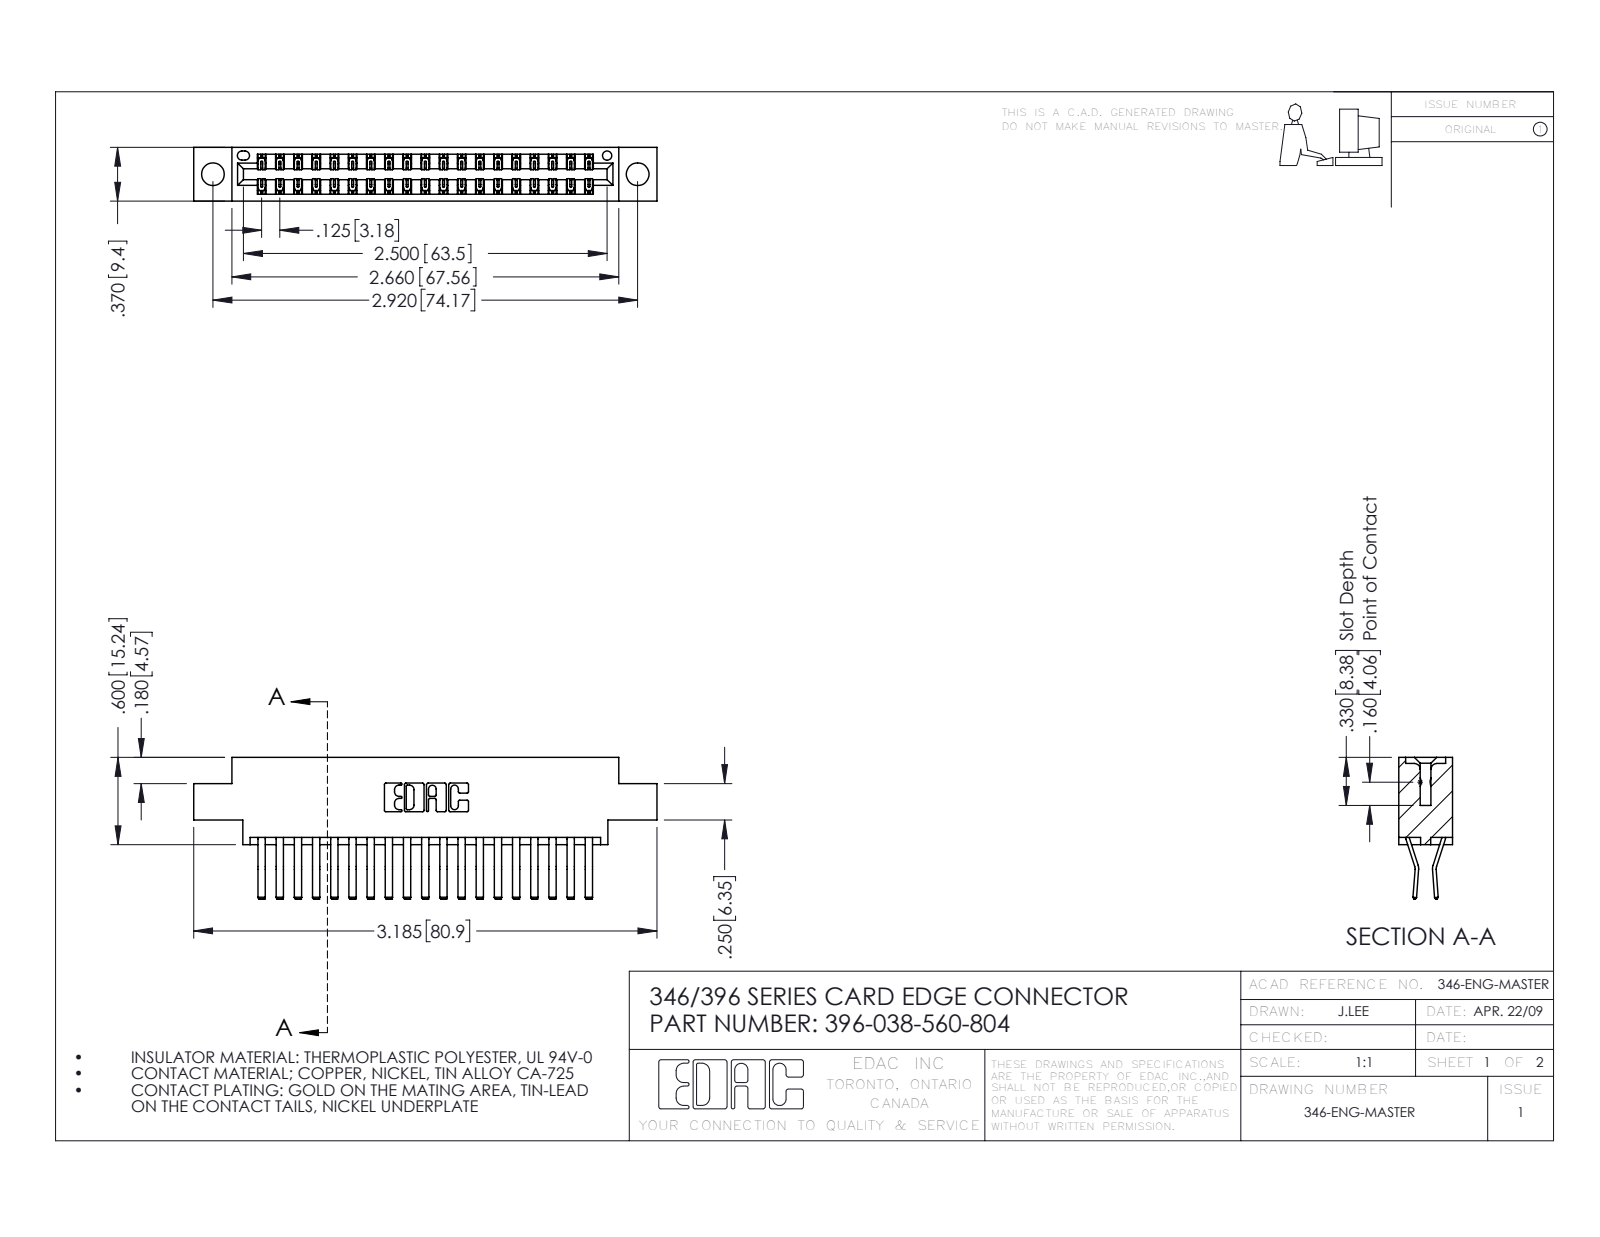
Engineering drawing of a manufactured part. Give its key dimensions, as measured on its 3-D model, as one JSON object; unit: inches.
{"part_name": "345-292-001_560 Tail; 396-038-560-804; 346 Part_0.170 Offset - 0.156 Dia-TH", "step_written_by": "SolidWorks 2016 (CONFIG_CONTROL_DESIGN)", "units": "inches", "bodies": {"solids": 39, "faces": 2178, "planar": 1410, "cylindrical": 768, "other": 0}, "overall_size": [3.185, 0.975, 0.37], "volume_in3": 0.471, "surface_area_in2": 16.9, "round_holes": [[0.156, 2], [0.064, 1]], "partial_cylinders_radius": [[0.006, 57], [0.01, 22], [0.007, 6], [0.031, 6], [0.026, 3], [0.01, 2], [0.014, 2], [0.022, 2]], "face_to_face_distances": [0.048, 0.322, 0.37, 0.25, 0.025, 0.072, 0.298, 0.275, 0.148, 0.222], "hole_center_spacings": [0.246, 2.713, 2.92]}
